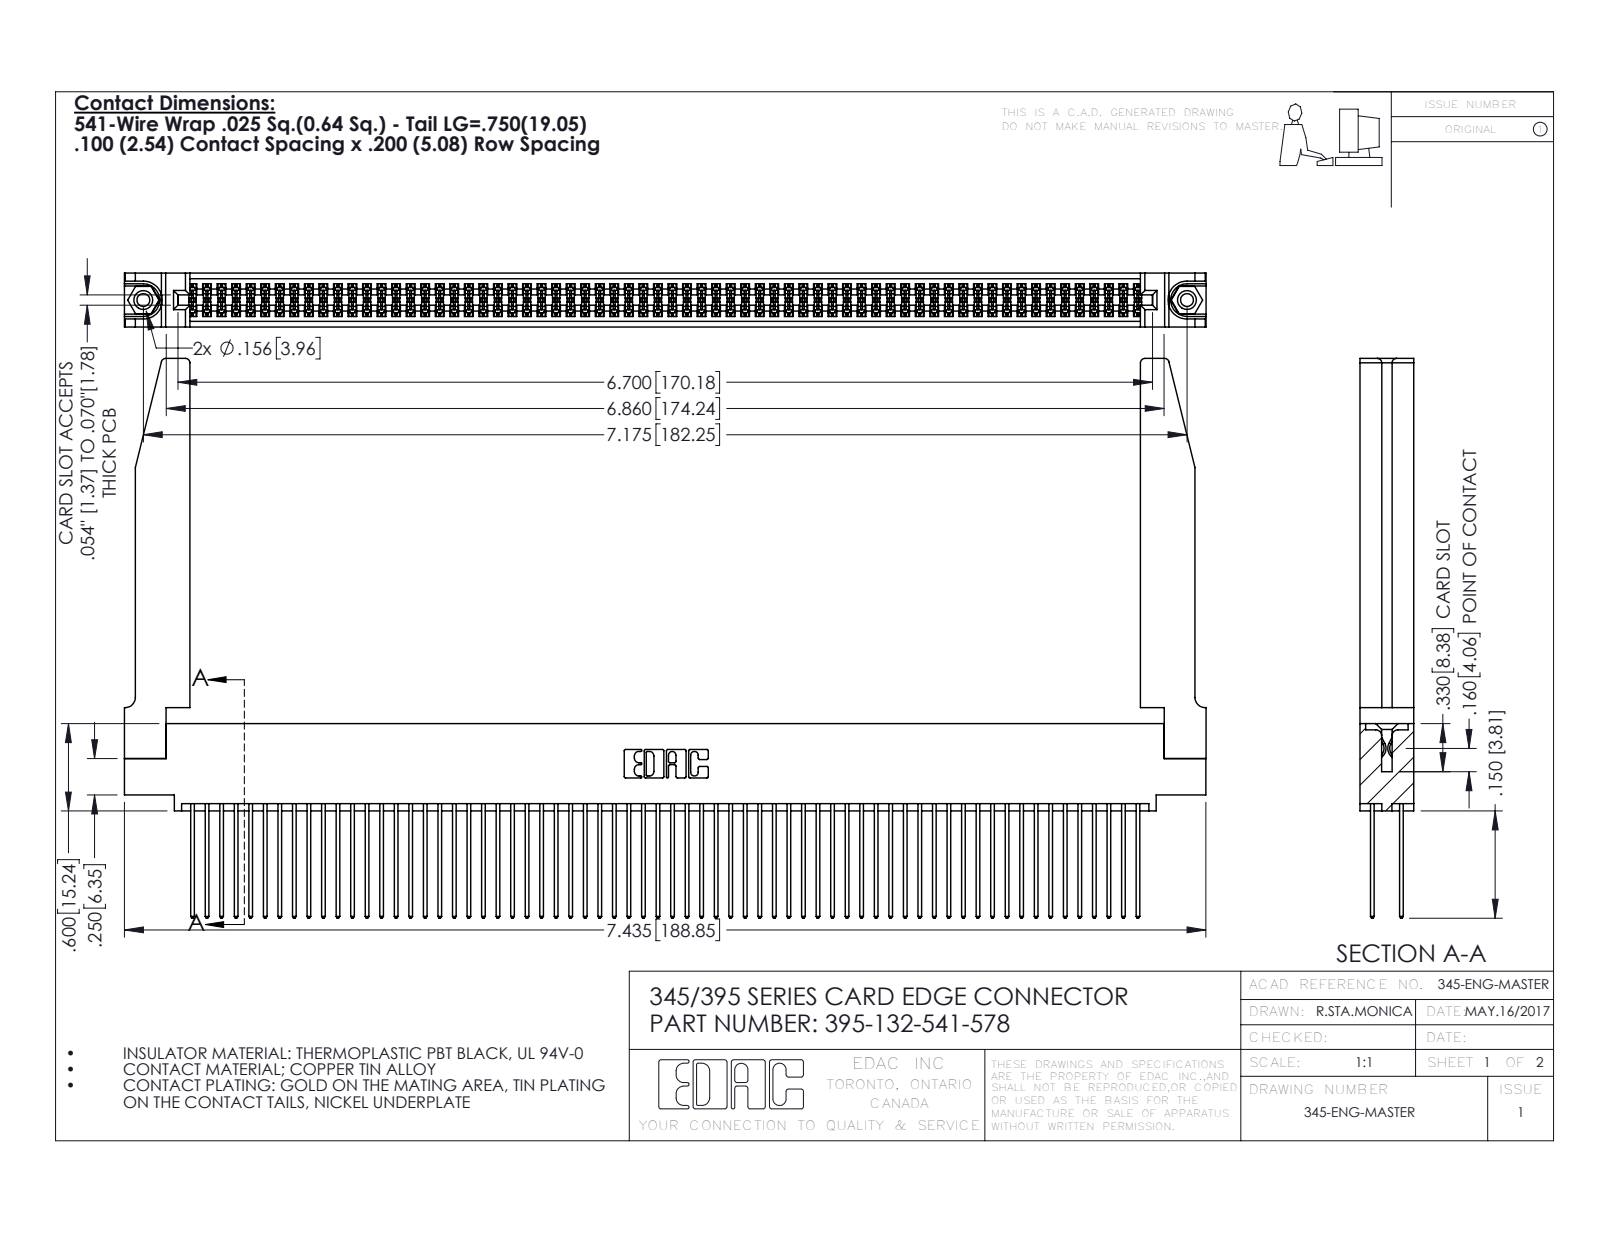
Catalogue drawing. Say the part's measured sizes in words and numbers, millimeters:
The part is named "345-250-001_345-250-001-102; 345 Part_0.110 Offset - 0.156 Dia-TH; 345-292-001_345-293-141; 395-132-541-578 (+1 more)". Its 3-D file was written by "SolidWorks 2016 (CONFIG_CONTROL_DESIGN)". It is 137 solids with 6964 faces: 4582 planar, 2330 cylindrical and 52 other. Overall it measures 188.9 by 97.7 by 9.4 millimeters. Its volume is 27 020 cubic millimeters and its surface area 39 420 square millimeters. Round holes: 2 of diameter 2.3, 2 of diameter 3.2, 2 of diameter 4, 1 of diameter 1.6. Round bosses or shafts: 2 of diameter 3.9. Partial cylindrical surfaces (rounded edges, fillets, slot ends): 198 of radius 0.2, 132 of radius 0.3, 22 of radius 0.3, 8 of radius 0.8, 6 of radius 0.2, 6 of radius 0.8, 3 of radius 0.7, 2 of radius 0.4. The main face-to-face distances are 1.8, 7.6, 2.5, 6.9, 0.6, 5.1, 9.4, 5.7, 4.4, 3.8. The hole center spacings are 6.9, 176.3, 182.2.
